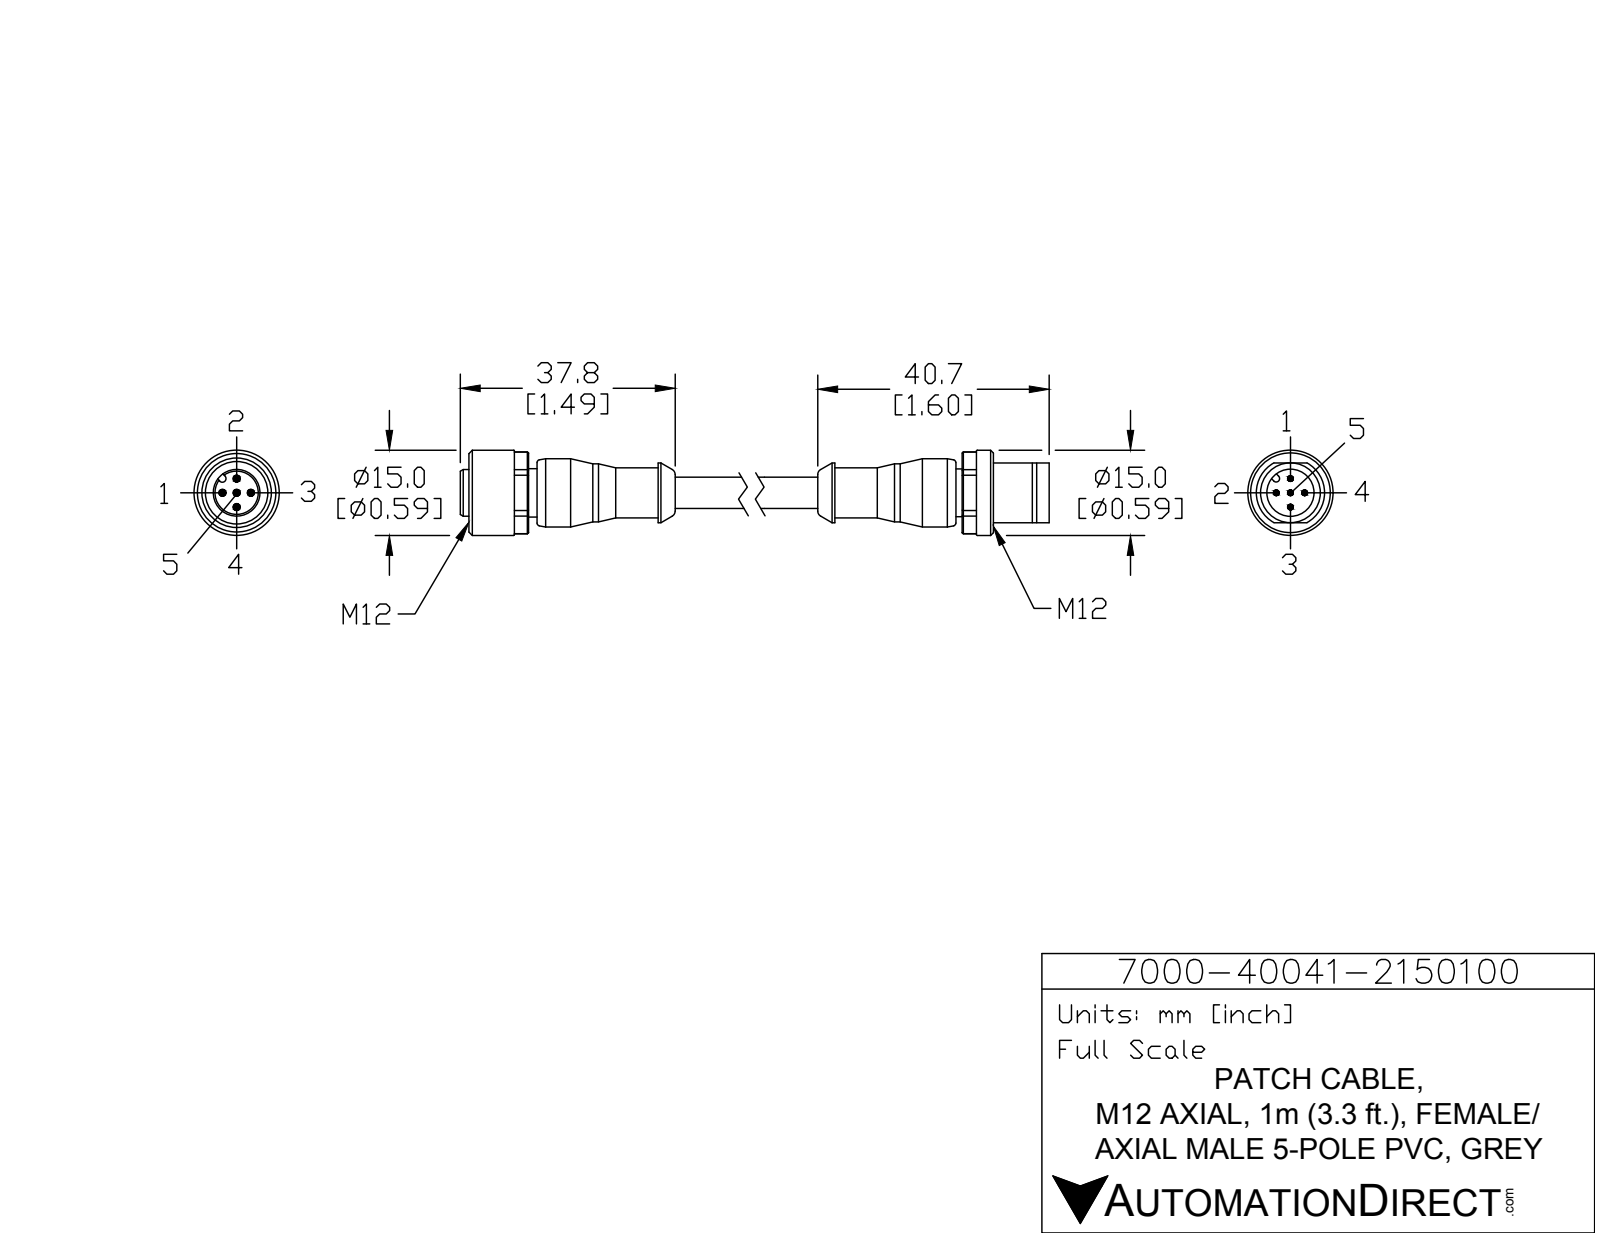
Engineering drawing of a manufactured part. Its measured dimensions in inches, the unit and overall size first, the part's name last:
Units: inches
Overall size (bounding box): 5.027 × 0.591 × 0.591
Round holes (diameter × count): ⌀0.047 ×5, ⌀0.327 ×1, ⌀0.433 ×1
Round bosses / shafts (diameter × count): ⌀0.039 ×5, ⌀0.591 ×1, ⌀0.472 ×1, ⌀0.413 ×1, ⌀0.402 ×1, ⌀0.346 ×1, ⌀0.335 ×1, ⌀0.331 ×1
Partial cylindrical surfaces — rounded edges, fillets, slot ends (radius × count): R0.024 ×1, R0.026 ×1, R0.283 ×1
Main face-to-face distances: 0.512, 0.118, 3.953, 0.413, 4.323, 0.472, 4.169, 0.295, 0.059, 0.098
Hole centre spacings: 0.098, 0.139, 0.197
Volume: 0.488 in³ · Surface area: 8.004 in²
Bodies: 2 solids, 196 faces (60 planar, 73 cylindrical, 63 other)
Part name (STEP PRODUCT): 7000-40041-2150100; 7000-40041-2150100_M; 7000-40041-2150100_F
STEP written by: SolidWorks 2018 (AUTOMOTIVE_DESIGN)
